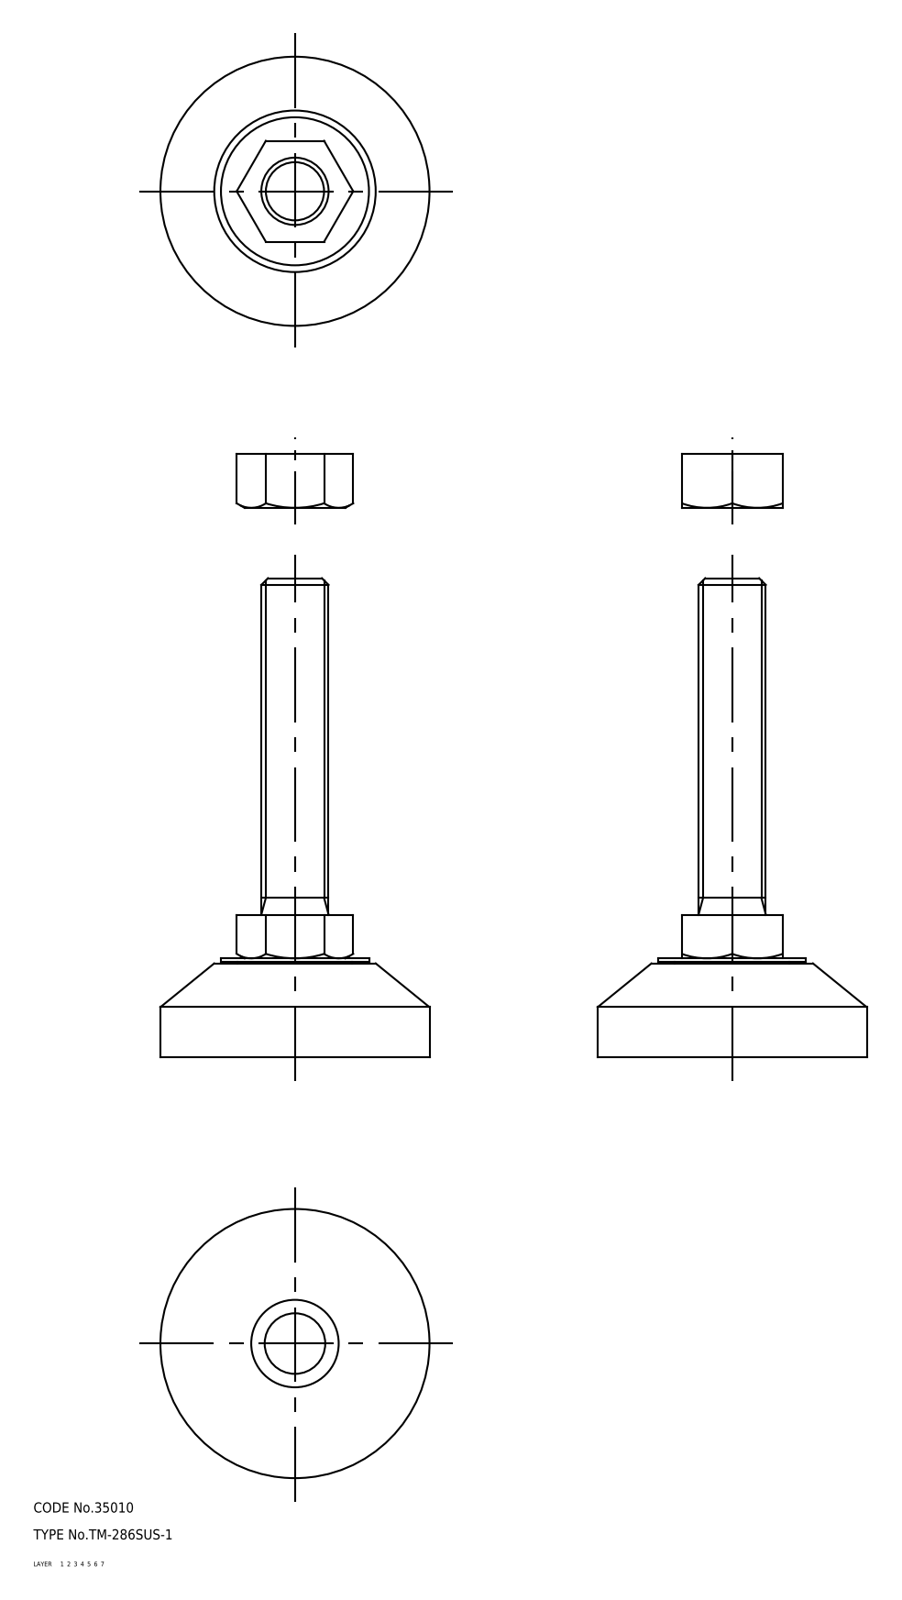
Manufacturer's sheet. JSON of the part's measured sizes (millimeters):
{"part_name": "67111642; 67111655", "step_written_by": "CADfix (AUTOMOTIVE_DESIGN)", "units": "millimeters", "bodies": {"solids": 2, "faces": 52, "planar": 0, "cylindrical": 0, "other": 52}, "overall_size": [142.5, 80, 80], "volume_mm3": 166436, "surface_area_mm2": 28215}
